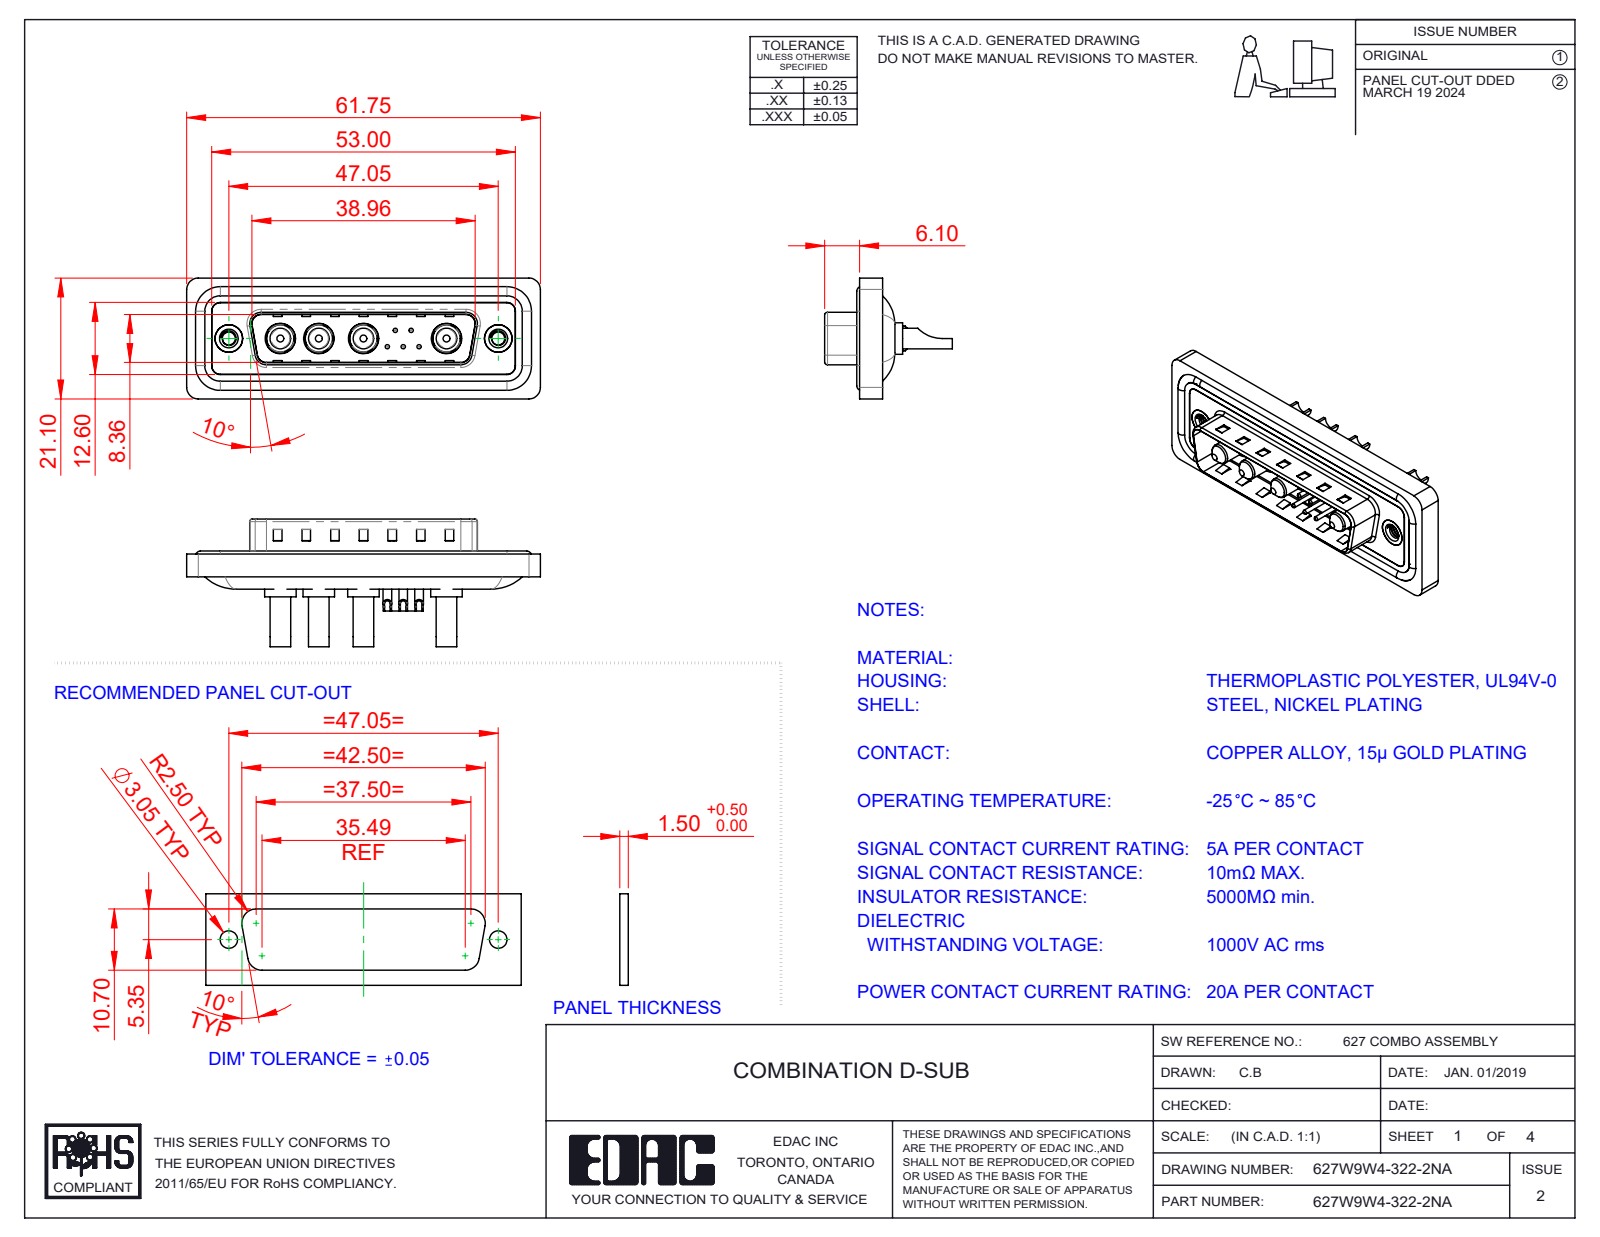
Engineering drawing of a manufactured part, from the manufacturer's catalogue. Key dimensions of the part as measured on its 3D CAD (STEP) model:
Part name (STEP PRODUCT): 627Combo Shell Front_25 Contacts; 627Combo Shell Rear_25 Contacts; 627Combo Contact Row 2_22; 627Combo Threaded Rivet_A (+5 more)
STEP written by: SolidWorks 2023 (CONFIG_CONTROL_DESIGN)
Units: millimetres
Bodies: 20 solids, 850 faces (306 planar, 358 cylindrical, 186 other)
Overall size (bounding box): 61.75 × 22.3 × 21.1
Volume: 7 465 mm³ · Surface area: 12 203 mm²
Round holes (diameter × count): ⌀0.75 ×5, ⌀1 ×5, ⌀1.6 ×5, ⌀2 ×5, ⌀2.7 ×4, ⌀4.85 ×4, ⌀5.3 ×4, ⌀2.26 ×2, ⌀4 ×2, ⌀4.8 ×2, ⌀5 ×2
Round bosses / shafts (diameter × count): ⌀1.5 ×5, ⌀5.5 ×4, ⌀5.2 ×4, ⌀4.75 ×4, ⌀3.75 ×4, ⌀3.6 ×4, ⌀1.6 ×4, ⌀4.9 ×2
Partial cylindrical surfaces — rounded edges, fillets, slot ends (radius × count): R1.5 ×22, R2 ×18, R0.5 ×8, R1.6 ×8, R1 ×6, R0.25 ×4, R0.6 ×4, R0.65 ×4
Main face-to-face distances: 0.4, 1.5, 1.1, 0.5, 1.6, 3.1, 2.9, 0.82, 9.58, 5.65
Hole centre spacings: 3.16, 2.77, 5.04, 14.51, 2.78, 4.4, 4.41, 5
